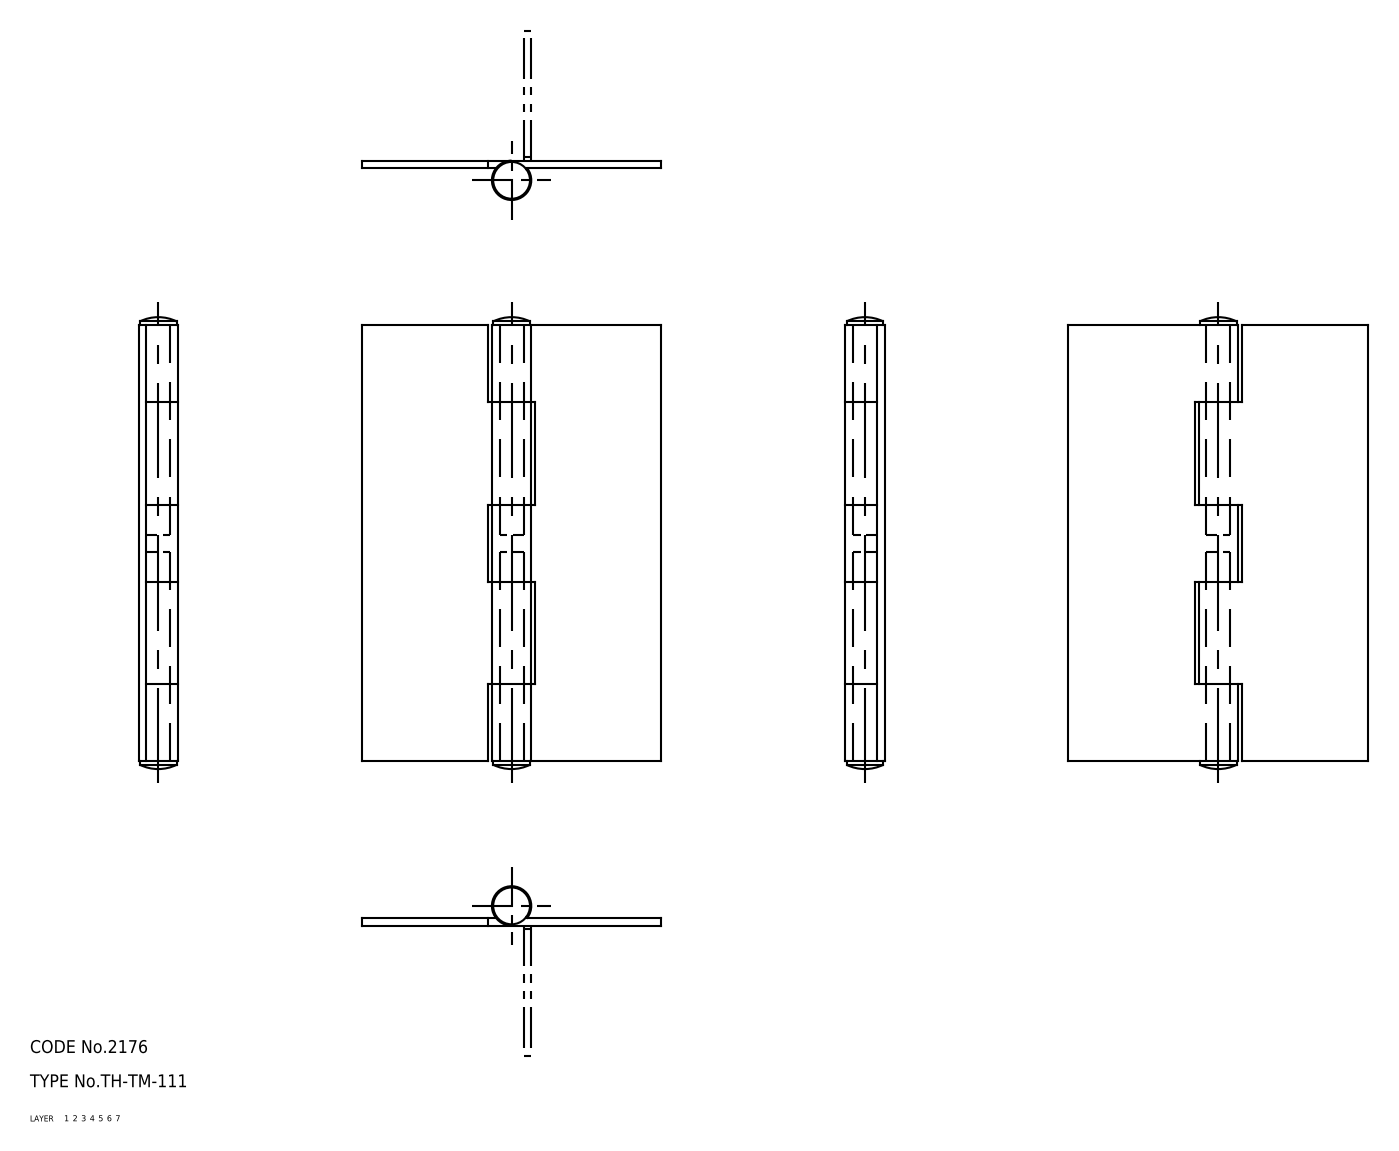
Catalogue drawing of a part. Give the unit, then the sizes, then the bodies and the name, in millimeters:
Units: millimetres
Overall size (bounding box): 105.6 × 70 × 9.2
Volume: 18 050 mm³ · Surface area: 20 609 mm²
Bodies: 4 solids, 52 faces (0 planar, 0 cylindrical, 52 other)
Part name (STEP PRODUCT): 67111516; 67111529; 67111542; 67111555
STEP written by: CADfix (AUTOMOTIVE_DESIGN)
